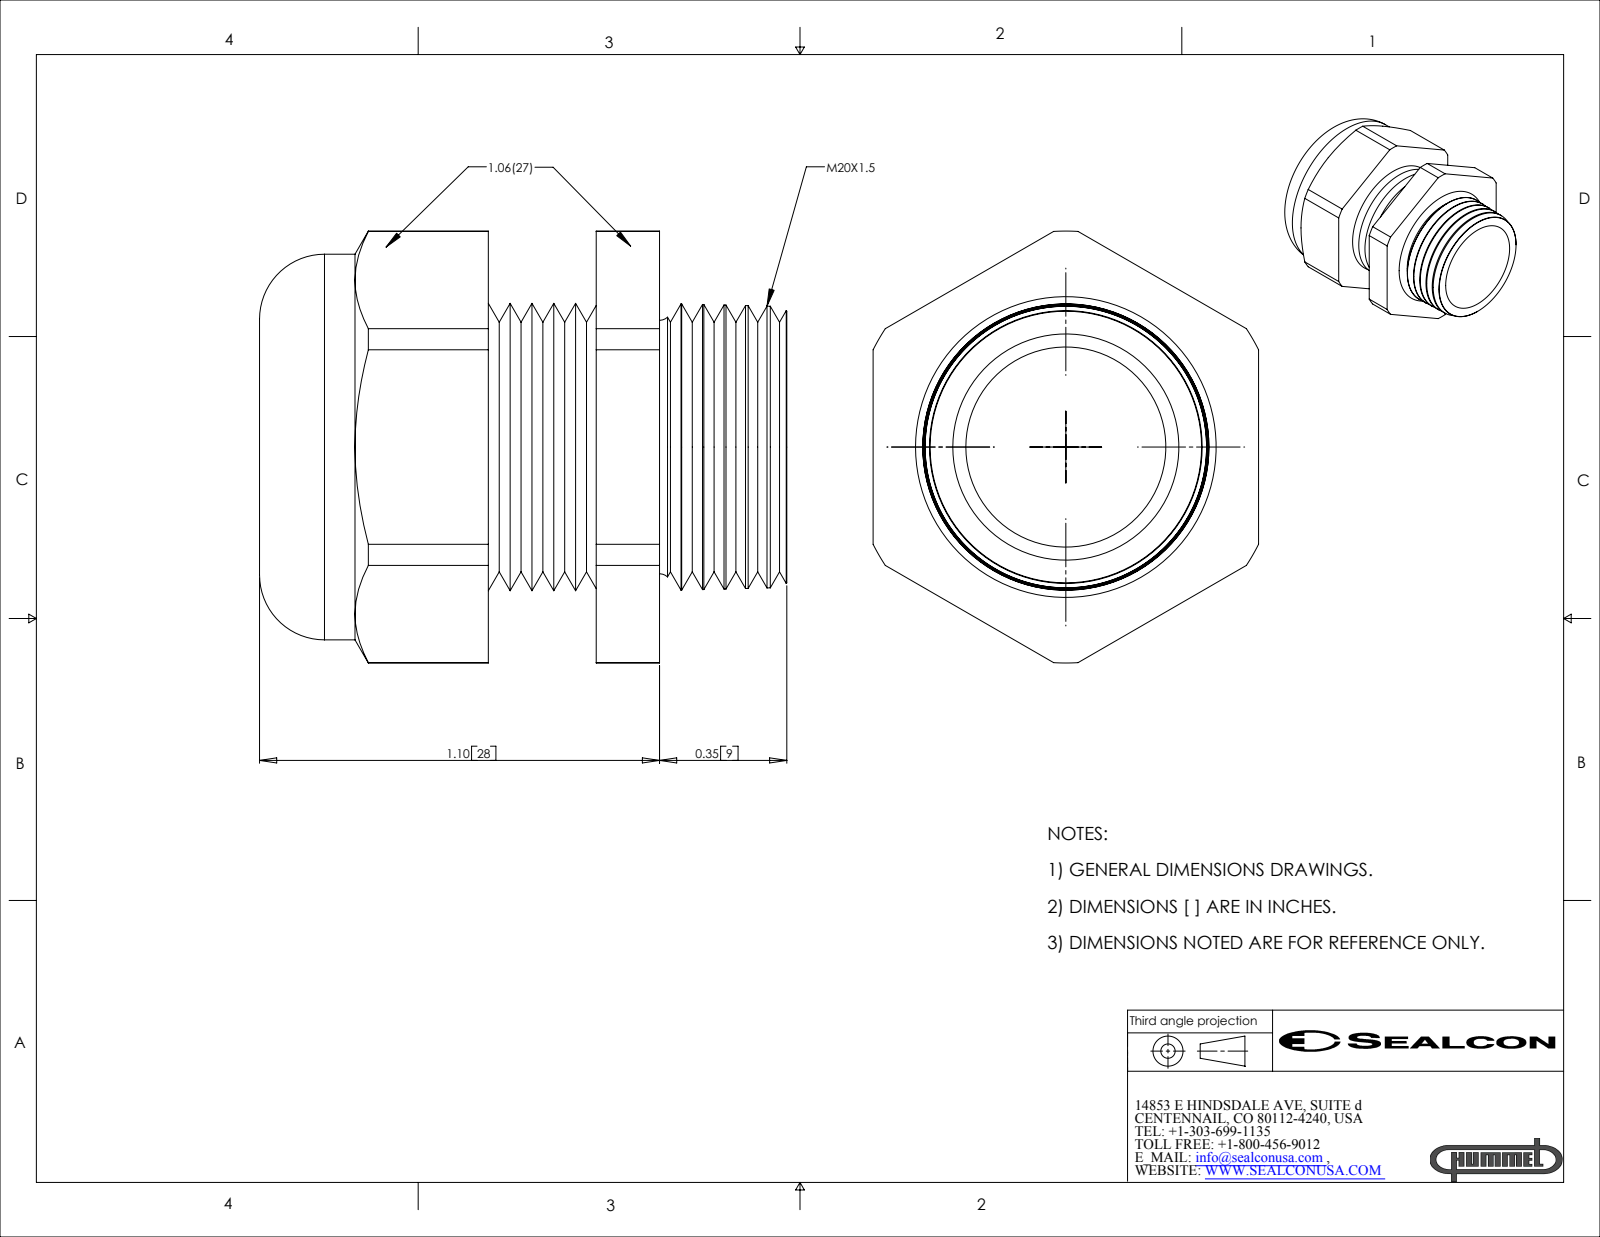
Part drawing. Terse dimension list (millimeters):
name: CD22MA-GY
written by: SolidWorks 2007 (CONFIG_CONTROL_DESIGN)
unit: mm
bodies: 2 solids, 116 faces (20 planar, 24 cylindrical, 72 other)
size: 36.8 × 30.1 × 26.9
volume: 10 300 mm³; area: 7 568 mm²
holes: 1× ⌀14, 1× ⌀17, 1× ⌀20.1
bosses: 1× ⌀26.9
rounds: 1× R15.1
face distances: 26.9, 7.5, 12, 4.4, 9.3, 16.8, 21.3, 30.1, 20.9, 13.3
